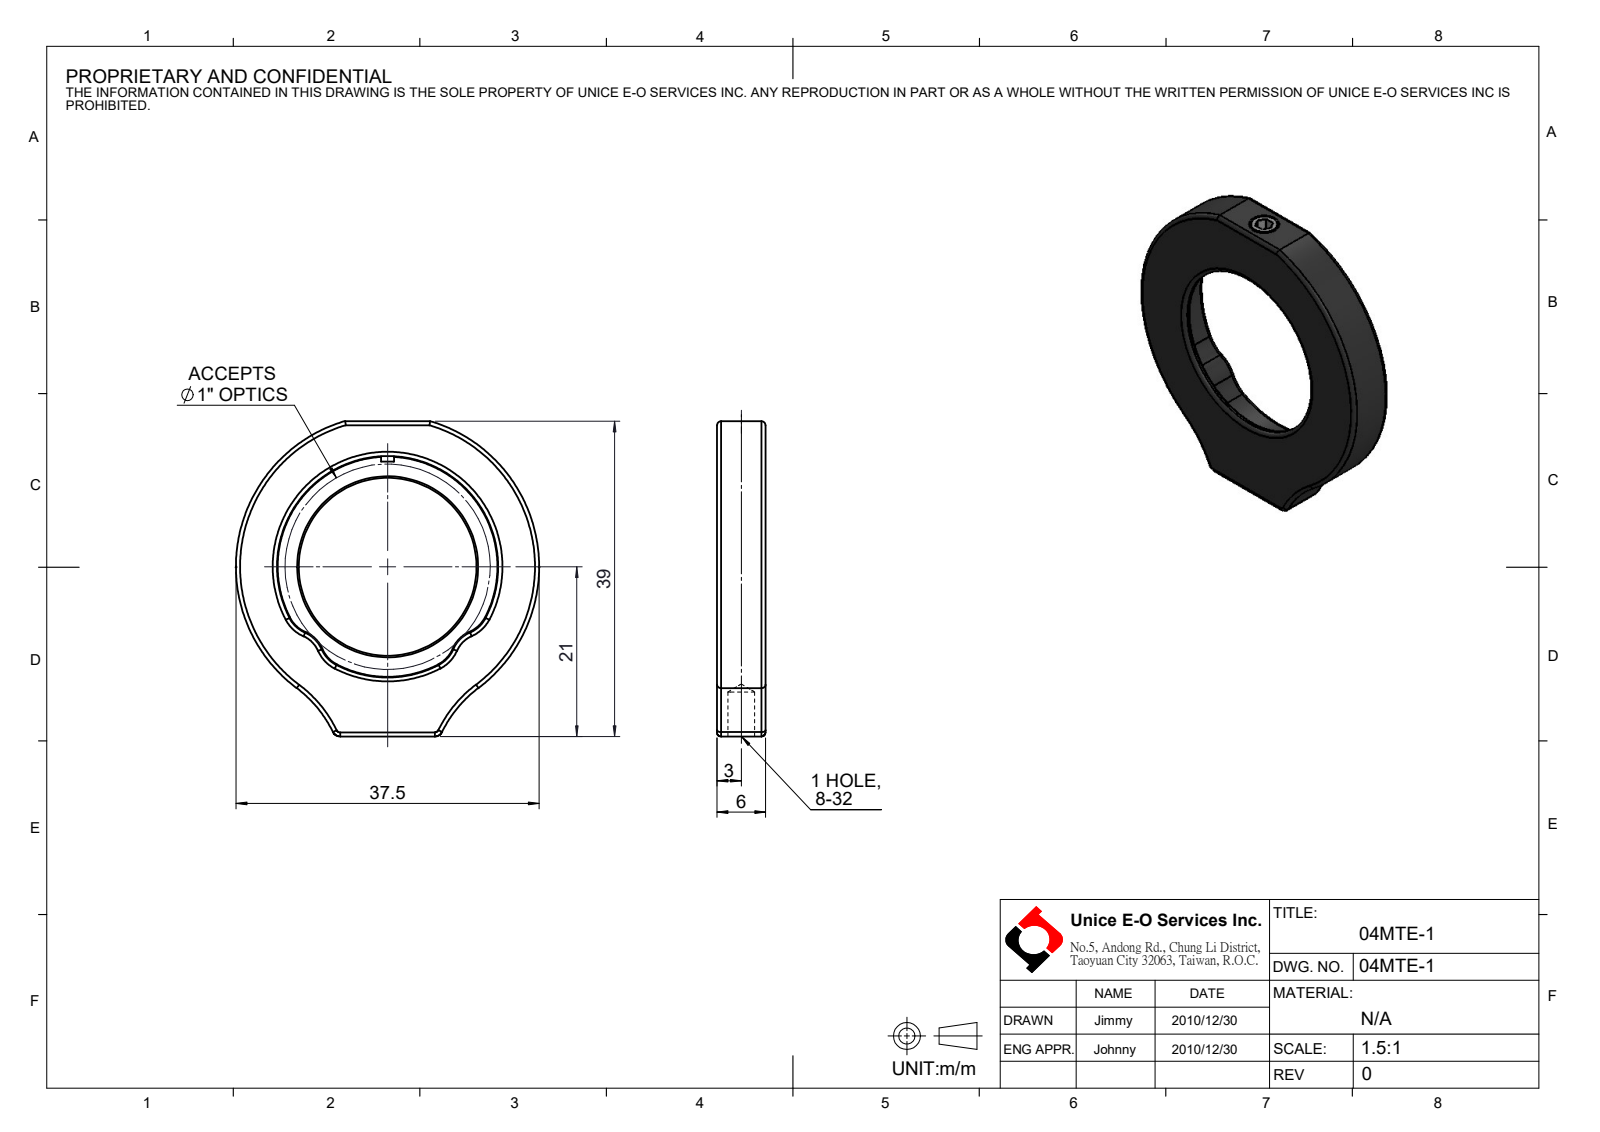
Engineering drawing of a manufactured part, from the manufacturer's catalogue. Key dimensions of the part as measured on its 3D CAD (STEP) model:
Part name (STEP PRODUCT): 04MTE-1
STEP written by: SolidWorks 2016 (CONFIG_CONTROL_DESIGN)
Units: millimetres
Bodies: 3 solids, 95 faces (16 planar, 33 cylindrical, 46 other)
Overall size (bounding box): 39 × 37.5 × 6
Volume: 3 498 mm³ · Surface area: 2 858 mm²
Round holes (diameter × count): ⌀1.5 ×1, ⌀3.3 ×1, ⌀3.45 ×1, ⌀22 ×1, ⌀27.4 ×1
Round bosses / shafts (diameter × count): ⌀4 ×1, ⌀1.6 ×1
Partial cylindrical surfaces — rounded edges, fillets, slot ends (radius × count): R4 ×6, R0.5 ×4, R1 ×2, R15 ×2, R18.75 ×1
Main face-to-face distances: 6, 1, 5, 39, 2, 35, 4, 2.5, 36.5, 1.5
